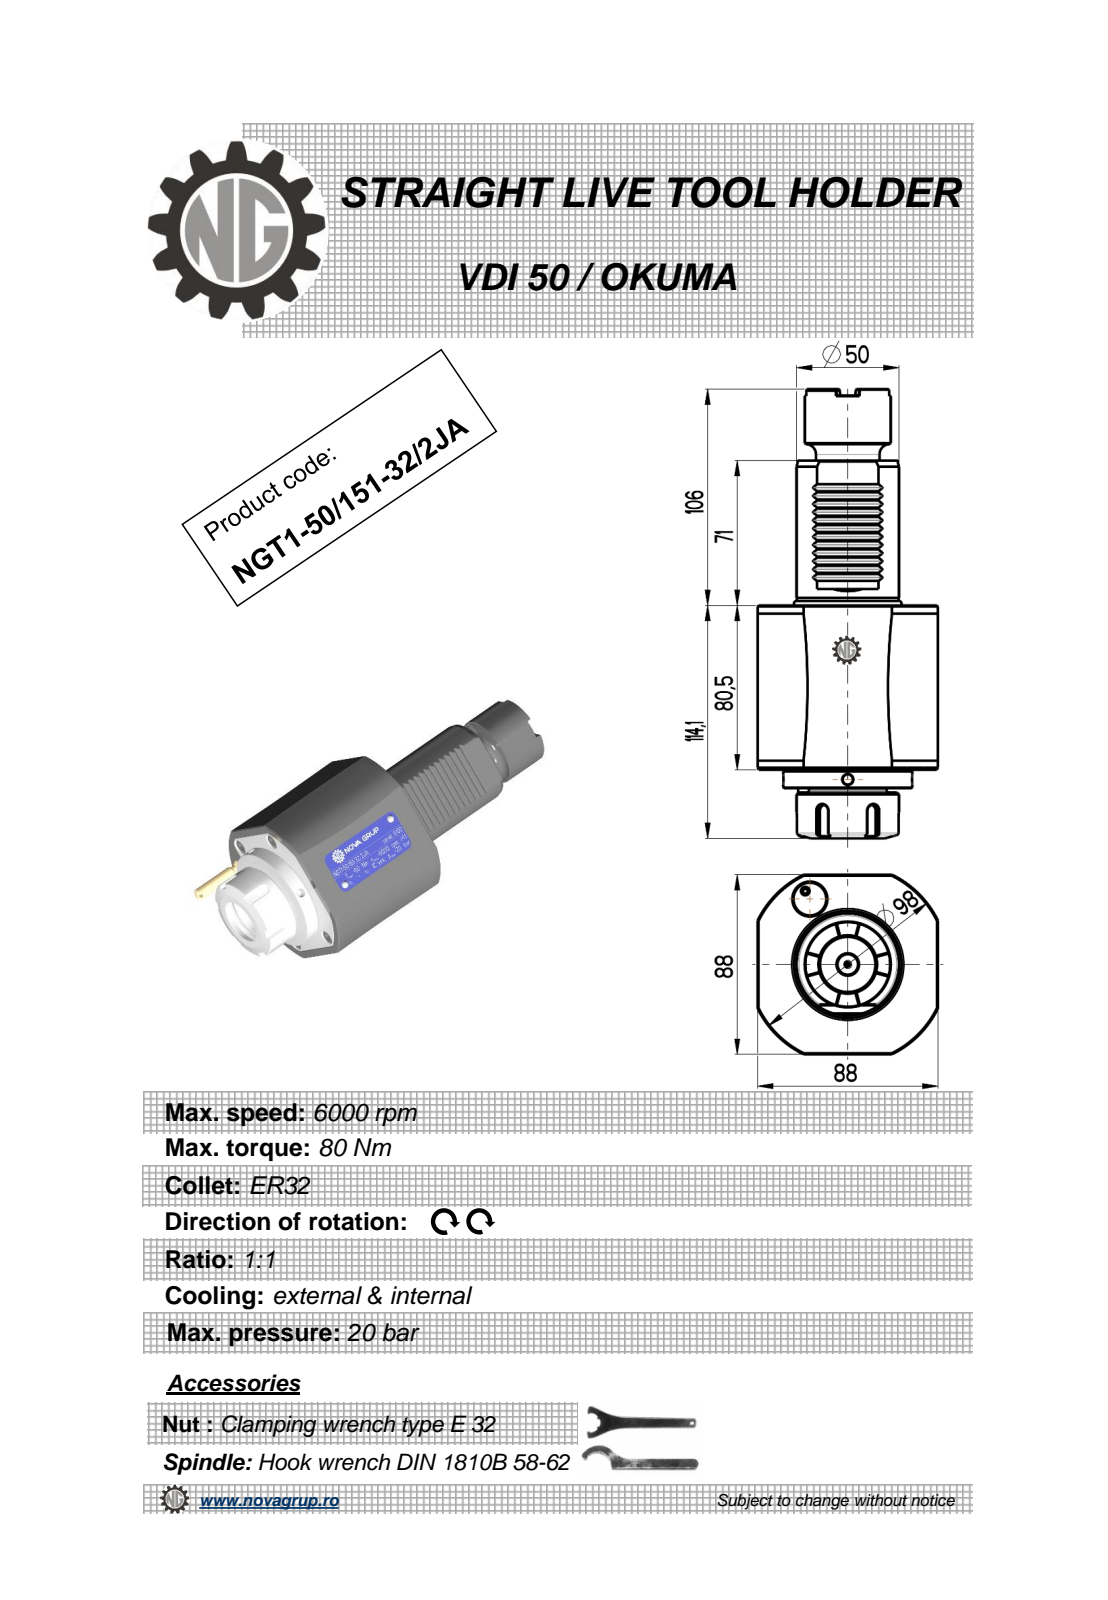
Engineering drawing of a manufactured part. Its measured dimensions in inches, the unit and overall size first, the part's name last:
Units: inches
Overall size (bounding box): 8.665 × 3.465 × 3.465
Round holes (diameter × count): ⌀0.197 ×2, ⌀0.098 ×1, ⌀0.118 ×1, ⌀1.063 ×1, ⌀1.102 ×1
Round bosses / shafts (diameter × count): ⌀2.48 ×1, ⌀2.012 ×1, ⌀1.969 ×1, ⌀1.654 ×1, ⌀1.614 ×1, ⌀1.22 ×1, ⌀0.354 ×1, ⌀0.276 ×1
Partial cylindrical surfaces — rounded edges, fillets, slot ends (radius × count): R0.012 ×12, R0.118 ×5, R1.929 ×1
Main face-to-face distances: 3.465, 3.169, 0.354, 3.524, 0.02, 0.111, 3.189, 0.335, 2.795, 5.965
Hole centre spacings: 1.634
Volume: 48.61 in³ · Surface area: 102.7 in²
Bodies: 1 solid, 313 faces (124 planar, 61 cylindrical, 128 other)
Part name (STEP PRODUCT): NGT1_50_141_32_1JA
STEP written by: PRO/ENGINEER BY PARAMETRIC TECHNOLOGY CORPORATION, 2010280 (CONFIG_CONTROL_DESIGN)
